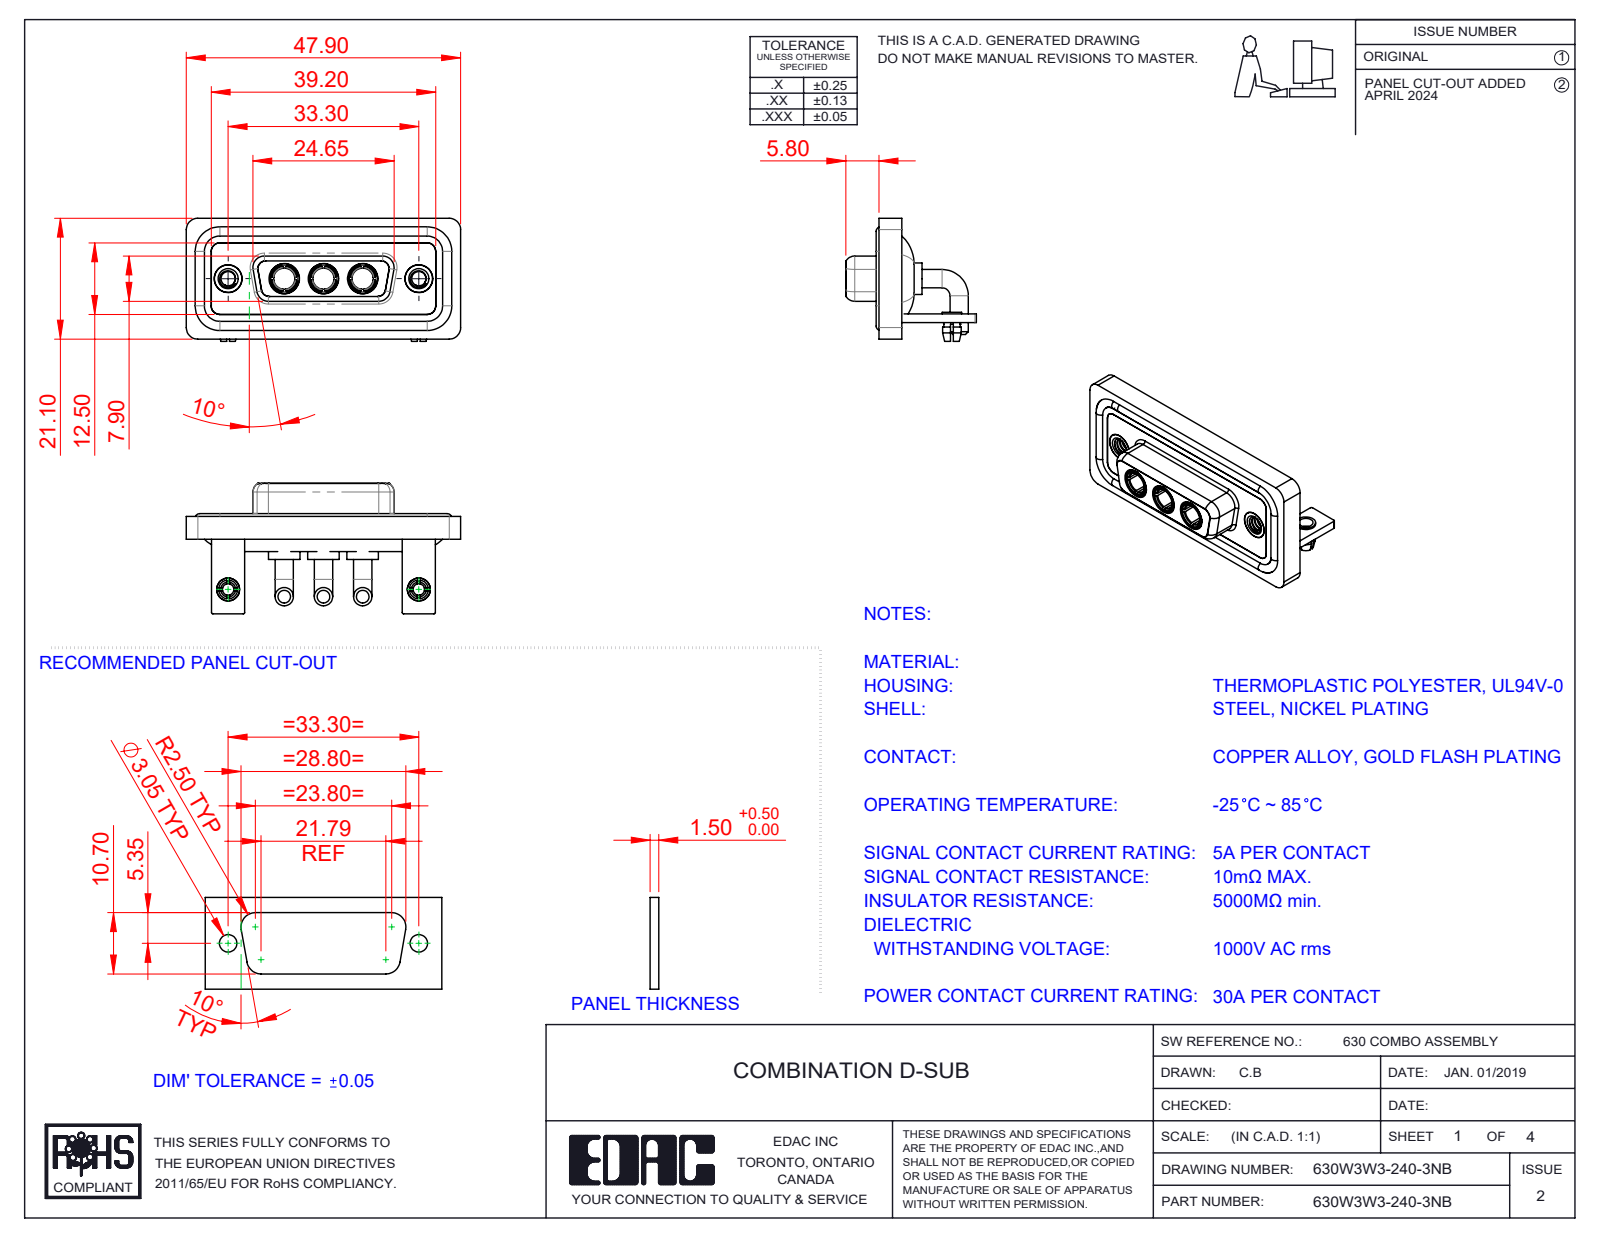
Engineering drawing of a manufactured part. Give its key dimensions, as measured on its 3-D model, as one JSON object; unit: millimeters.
{"part_name": "Power Socket_30A RA; 630Combo Shell Front_15 Contacts; 630Combo Shell Rear_15 Contacts; 630W3W3-140-3NB (+5 more)", "step_written_by": "SolidWorks 2023 (CONFIG_CONTROL_DESIGN)", "units": "millimeters", "bodies": {"solids": 17, "faces": 754, "planar": 260, "cylindrical": 317, "other": 177}, "overall_size": [47.9, 22.8, 21.5], "volume_mm3": 6659, "surface_area_mm2": 10976, "round_holes": [[4.85, 5], [2.5, 4], [3.7, 3], [5.3, 3], [2, 2], [3.2, 2], [4, 2], [4.05, 2], [5, 2]], "round_bosses_or_shafts": [[3.2, 6], [1.6, 4], [5.5, 3], [5.2, 3], [4.96, 3], [4.75, 3], [3.75, 3], [4.95, 2]], "partial_cylinders_radius": [[2, 21], [1.5, 18], [0.25, 16], [1.35, 12], [1.6, 8], [0.5, 5], [0.6, 4], [0.65, 4]], "face_to_face_distances": [0.4, 2.9, 1.5, 1.8, 3.7, 1.1, 4.1, 1.6, 2.5, 1.4], "hole_center_spacings": [6.85, 9.8, 16.65, 23.5, 33.3, 13.7]}
